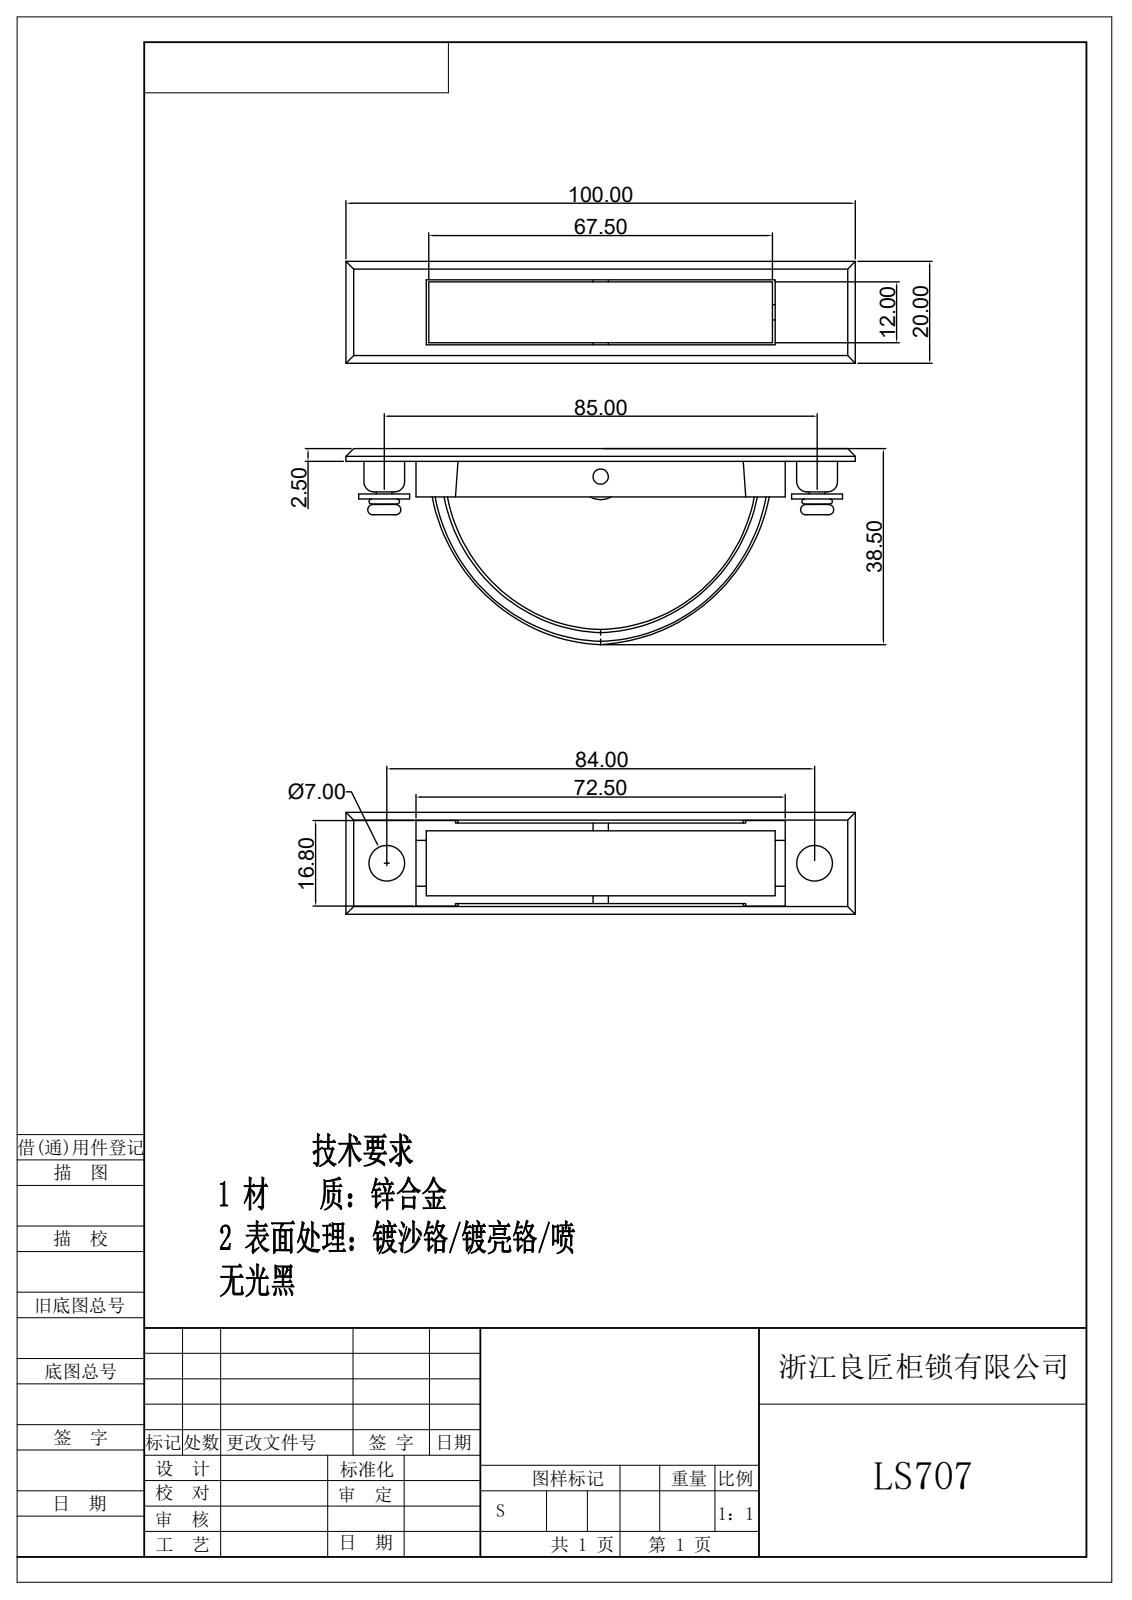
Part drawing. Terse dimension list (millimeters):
written by: Rhino 8.5 (AP203_CONFIGURATION_CONTROLLED_3D_DESIGN_OF_MECHANICAL_PARTS_AND_ASSEMBLIES_MIM_LF)
unit: mm
bodies: 11 solids, 289 faces (148 planar, 89 cylindrical, 52 other)
size: 100 × 38.5 × 20
volume: 10 814 mm³; area: 12 243 mm²
holes: 2× ⌀4.2, 1× ⌀3
bosses: 2× ⌀10, 2× ⌀7, 2× ⌀3.08
rounds: 4× R1.5, 4× R2, 4× R3.5, 4× R4, 1× R2.5, 1× R4.5
face distances: 0.5, 1.5, 2.5, 14.3, 3, 12.8, 1.9, 12.4, 13.9, 0.4
hole spacings: 85
